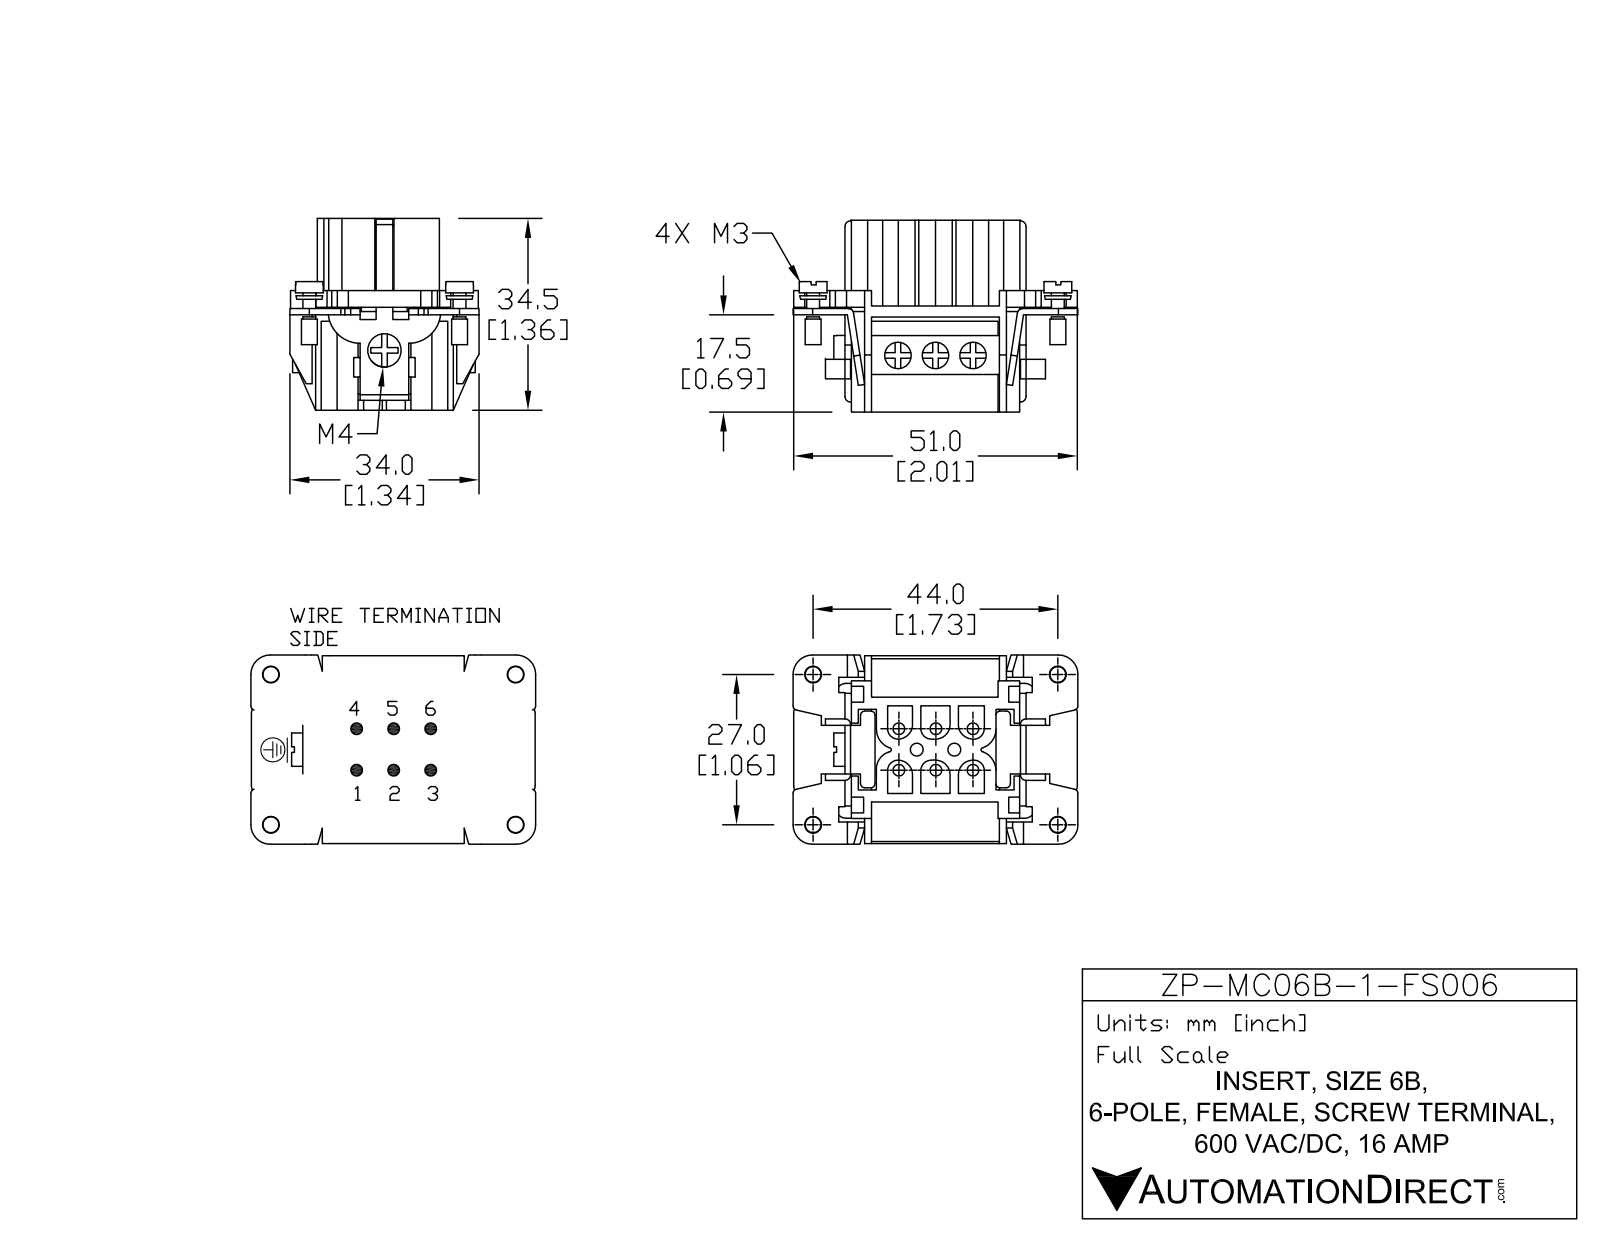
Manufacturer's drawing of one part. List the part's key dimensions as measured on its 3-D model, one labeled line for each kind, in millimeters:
Part name (STEP PRODUCT): ZP-6B-6-FS-INSERT
STEP written by: SolidWorks 2011 (AUTOMOTIVE_DESIGN)
Units: millimetres
Bodies: 9 solids, 757 faces (575 planar, 138 cylindrical, 44 other)
Overall size (bounding box): 51.2 × 34.41 × 34
Volume: 17 430 mm³ · Surface area: 18 295 mm²
Round holes (diameter × count): ⌀2.09 ×6, ⌀3.01 ×4, ⌀4.75 ×3, ⌀1.75 ×2, ⌀2.3 ×2, ⌀3 ×1
Round bosses / shafts (diameter × count): ⌀5 ×4, ⌀2.85 ×4, ⌀2.3 ×4, ⌀6 ×1
Partial cylindrical surfaces — rounded edges, fillets, slot ends (radius × count): R1 ×14, R0.75 ×12, R2 ×8, R1.86 ×6, R2.62 ×6, R3.5 ×4, R5.75 ×3, R0.37 ×2
Main face-to-face distances: 1.15, 2.75, 3, 4.75, 7, 2.29, 2.5, 0.46, 7.75, 14.75
Hole centre spacings: 6.66, 6.75, 9.99, 7.45, 22.99, 4.9, 4.96, 5.03
